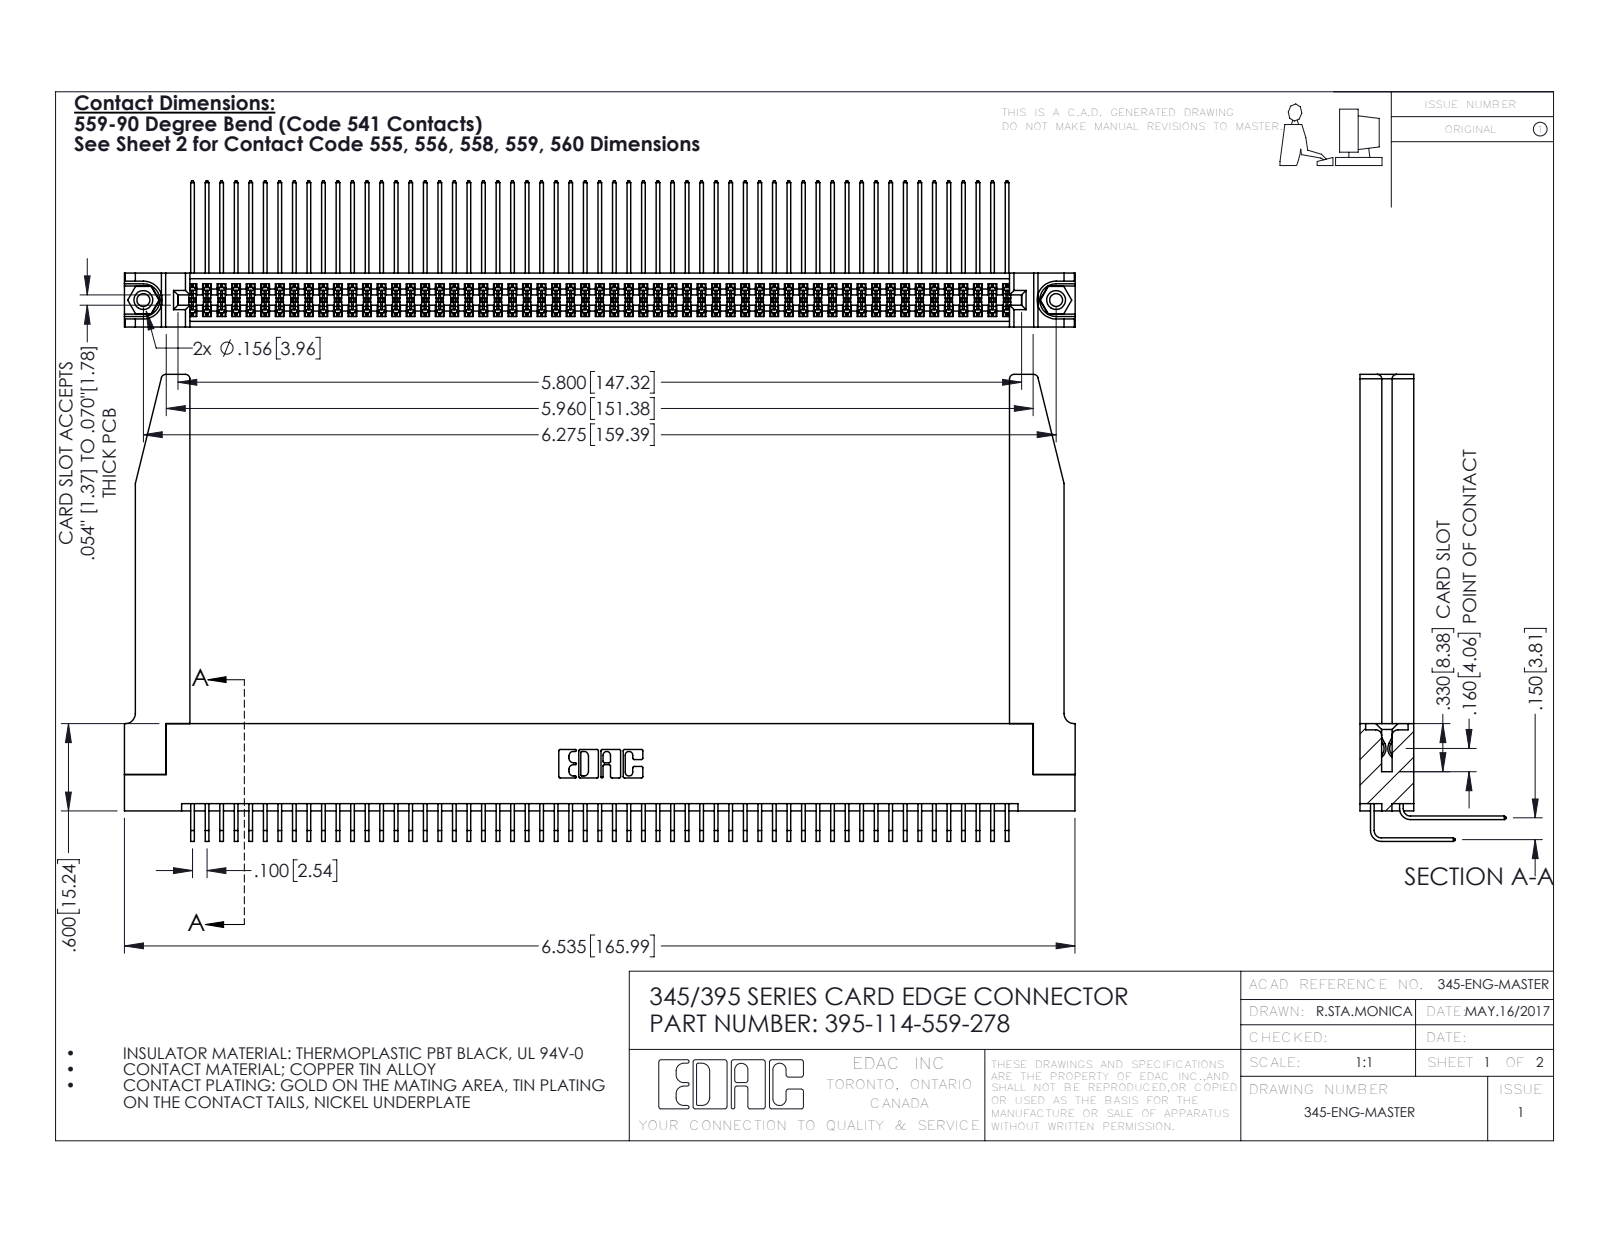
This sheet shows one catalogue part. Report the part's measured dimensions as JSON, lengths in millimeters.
{"part_name": "345-250-001_345-250-001-102; 345 Part_Flush Mounting Lugs - 0.156 Dia-TH; 395-114-559-278; 345-220-078_345-220-078 (+2 more)", "step_written_by": "SolidWorks 2016 (CONFIG_CONTROL_DESIGN)", "units": "millimeters", "bodies": {"solids": 119, "faces": 6288, "planar": 4212, "cylindrical": 2024, "other": 52}, "overall_size": [166, 81.5, 25.5], "volume_mm3": 24700, "surface_area_mm2": 35240, "round_holes": [[2.3, 2], [3.2, 2], [4, 2], [1.6, 1]], "round_bosses_or_shafts": [[3.9, 2]], "partial_cylinders_radius": [[0.2, 171], [0.3, 22], [0.8, 8], [0.2, 6], [0.8, 6], [0.7, 3], [0.4, 2], [0.5, 2]], "face_to_face_distances": [1.8, 7.6, 9.4, 5.1, 2.5, 6.9, 0.6, 5.7, 4.4, 3.8], "hole_center_spacings": [6.9, 153.4, 159.4]}
